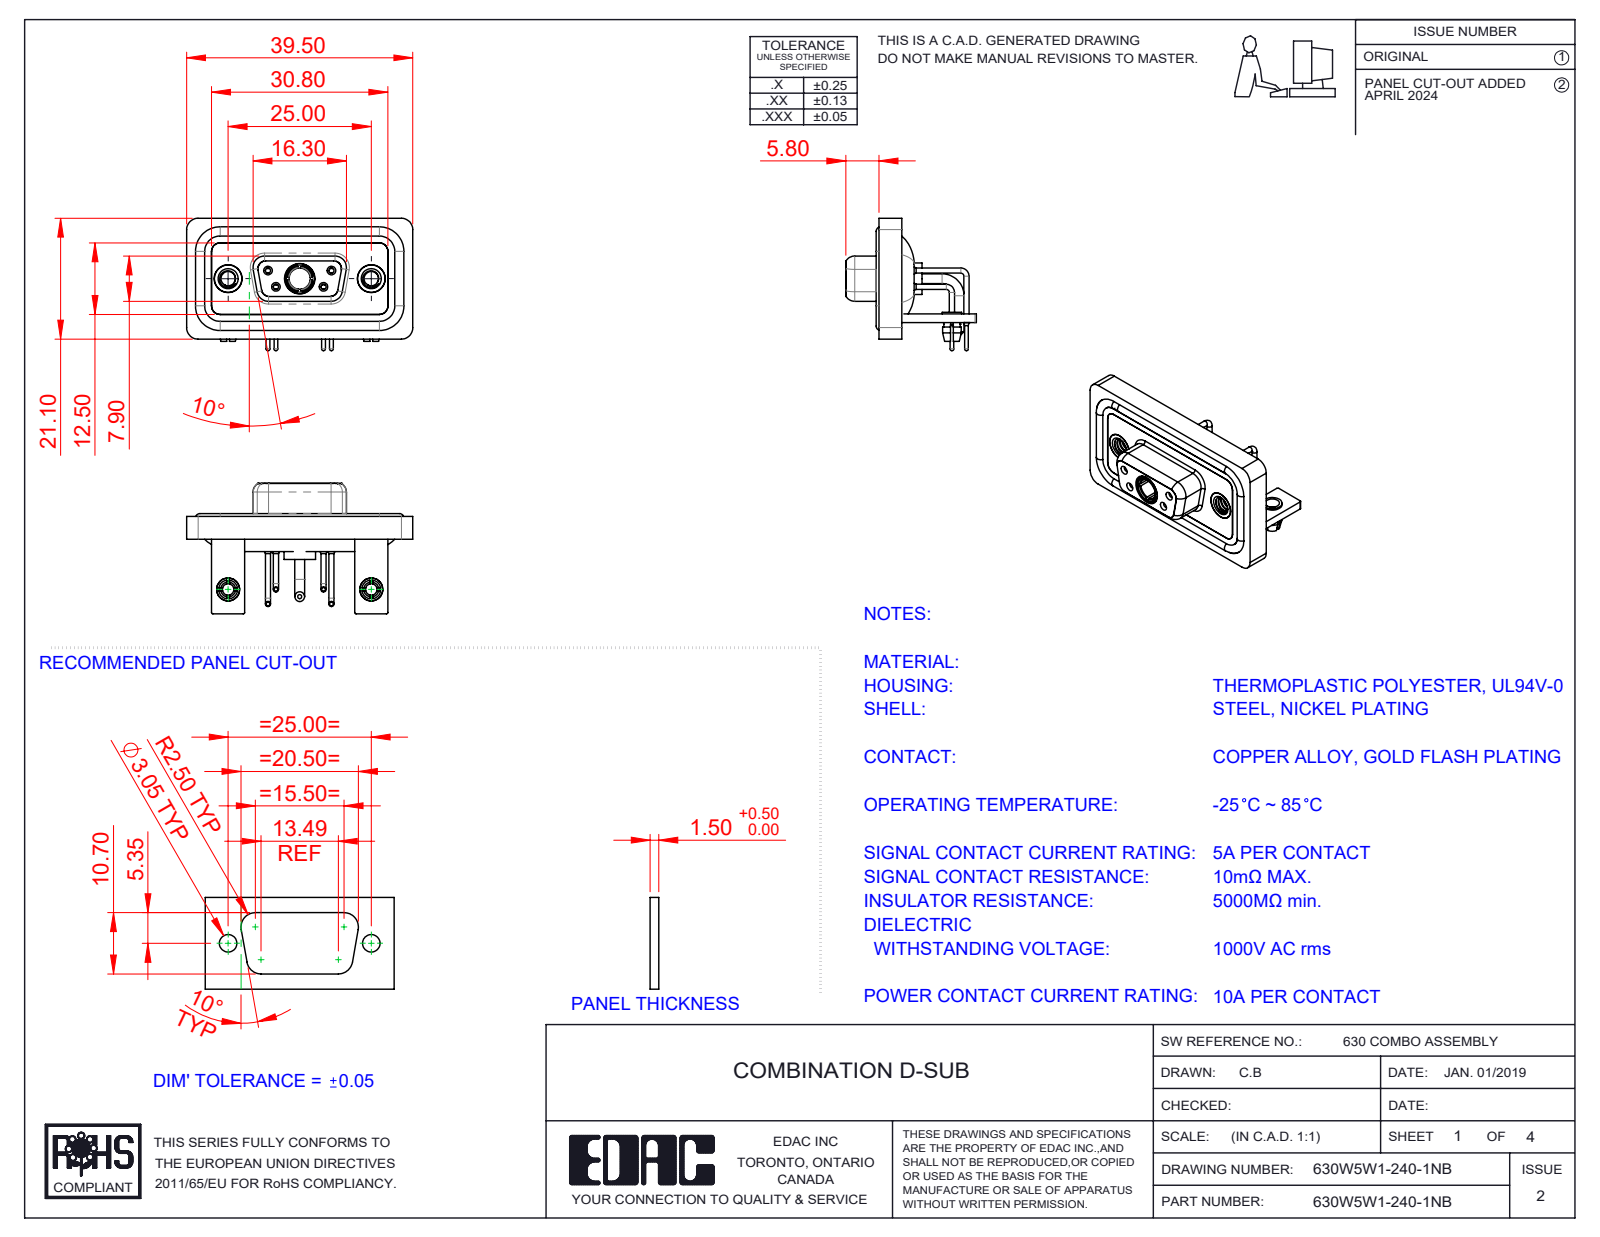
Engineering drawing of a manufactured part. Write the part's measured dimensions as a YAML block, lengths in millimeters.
part_name: "630Combo Threaded Rivet_A; Power Socket_10A RA; 630Combo Shell Rear_09 Contacts; 630Combo Waterproof Housing_09 Contacts (+7 more)"
step_written_by: "SolidWorks 2023 (CONFIG_CONTROL_DESIGN)"
units: millimeters
bodies: {solids: 17, faces: 810, planar: 262, cylindrical: 359, other: 189}
overall_size: [39.5, 23.12, 22.8]
volume: 5166
surface_area: 8742
round_holes:
  - {diameter: 2, count: 6}
  - {diameter: 0.9, count: 4}
  - {diameter: 1.1, count: 4}
  - {diameter: 1.5, count: 4}
  - {diameter: 2.5, count: 4}
  - {diameter: 4.85, count: 3}
  - {diameter: 1.6, count: 2}
  - {diameter: 1.7, count: 2}
  - {diameter: 3.2, count: 2}
  - {diameter: 4, count: 2}
  - {diameter: 4.05, count: 2}
  - {diameter: 5, count: 2}
round_bosses_or_shafts:
  - {diameter: 1.6, count: 6}
  - {diameter: 0.9, count: 4}
  - {diameter: 0.65, count: 4}
  - {diameter: 4.95, count: 2}
  - {diameter: 4.8, count: 2}
  - {diameter: 4, count: 2}
  - {diameter: 3.4, count: 2}
  - {diameter: 3.3, count: 2}
partial_cylinders:
  - {radius: 2, count: 19}
  - {radius: 1.5, count: 18}
  - {radius: 0.25, count: 16}
  - {radius: 1.35, count: 8}
  - {radius: 1.6, count: 8}
  - {radius: 0.5, count: 5}
  - {radius: 0.6, count: 4}
  - {radius: 0.65, count: 4}
face_to_face_distances: [0.4, 2.9, 1.5, 1.8, 1.1, 3.7, 1.6, 0.8, 2.5, 3.1]
hole_center_spacings: [3.16, 5.72, 7.1, 12.5, 18.1, 25, 4.39, 4.4]
